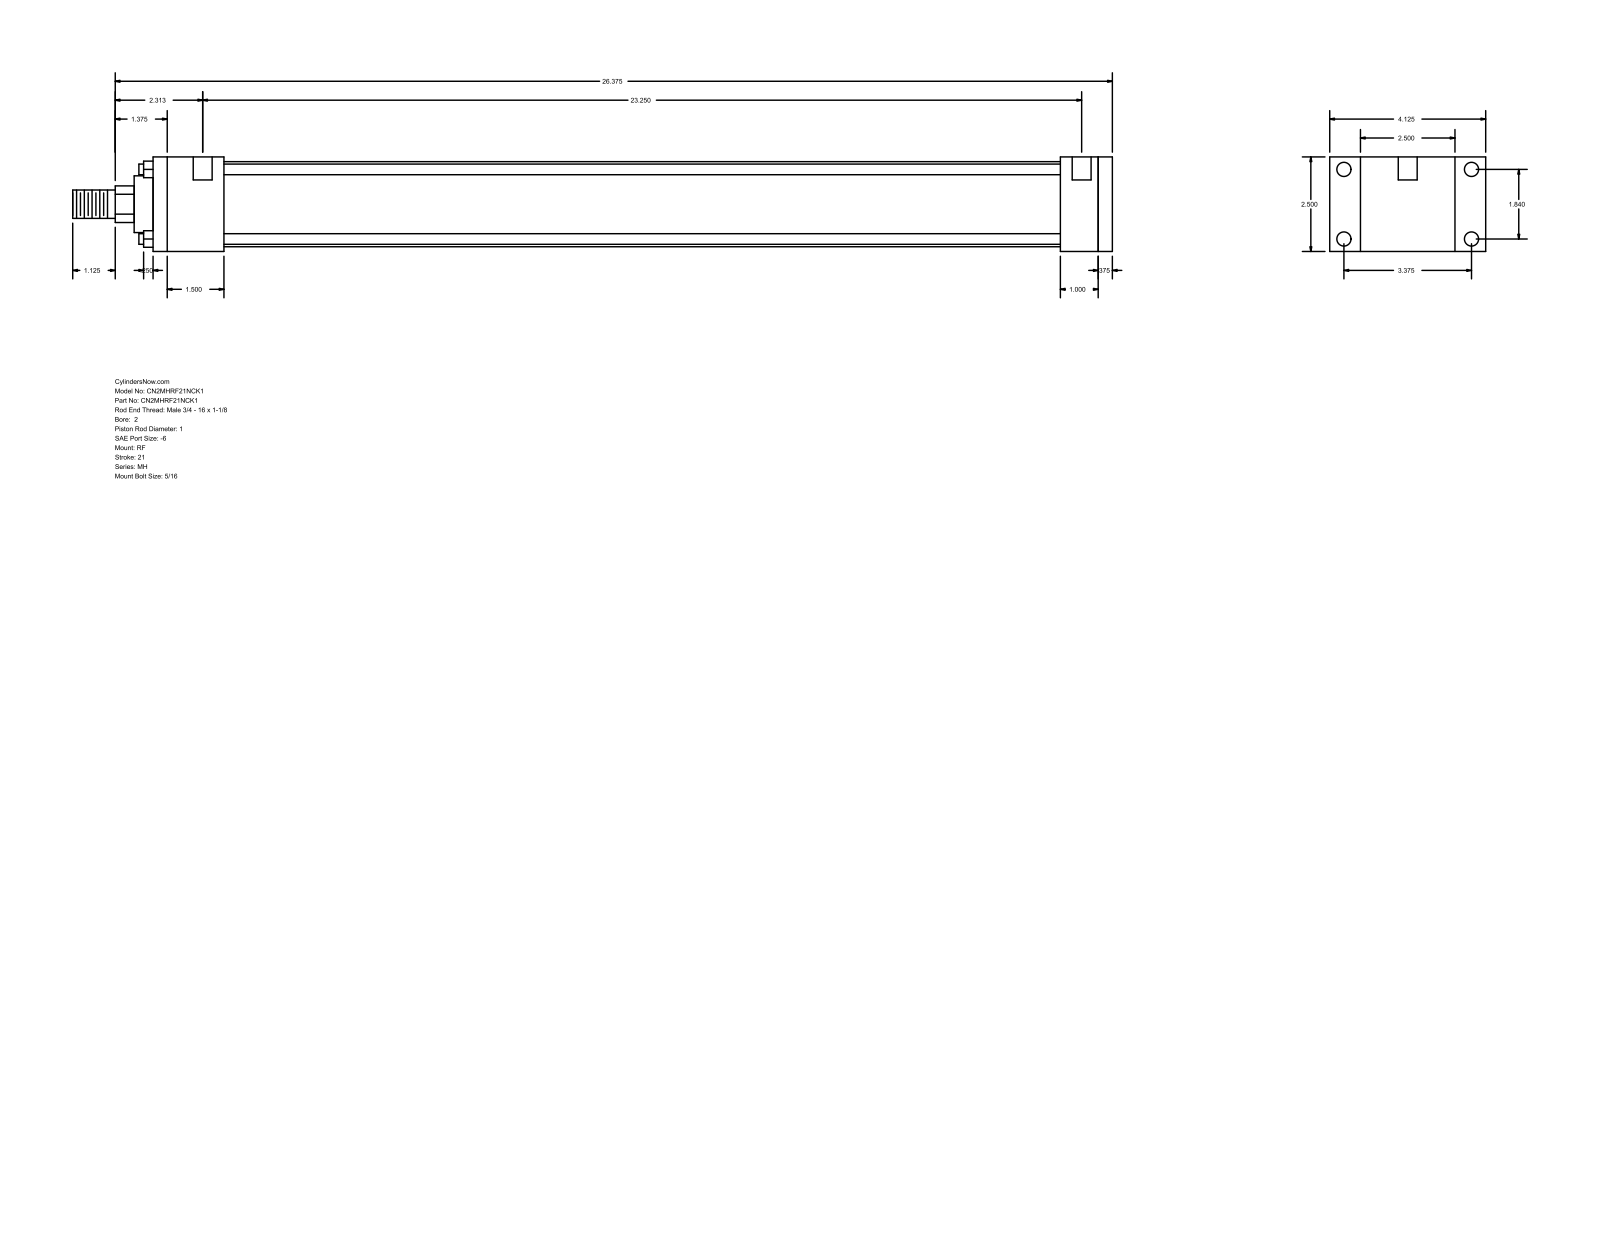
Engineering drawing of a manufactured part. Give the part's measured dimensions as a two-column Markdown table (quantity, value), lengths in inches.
| quantity | value |
| --- | --- |
| part name | MH_RF__0200_1 |
| STEP written by | GSSL Pune (CONFIG_CONTROL_DESIGN) |
| units | inches |
| bodies | 0 solids, 92 faces (64 planar, 28 cylindrical, 0 other) |
| overall size | 27.5 × 4.125 × 2.5 |
| round holes (diameter × count) | 0.219 × 4, 0.375 × 4, 0.5 × 2 |
| round bosses / shafts (diameter × count) | 0.281 × 4, 2.25 × 1, 1.5 × 1, 1 × 1, 0.75 × 1 |
| partial cylindrical surfaces (radius × count) | 0.484 × 1 |
| main face-to-face distances | 2.5, 25.375, 0.375, 25, 0.813, 1, 1.875, 24, 22.125, 23.125 |
| hole center spacings | 1.84, 3.375, 3.844, 23.562, 0.125, 0.187, 23.25, 23.375 |
